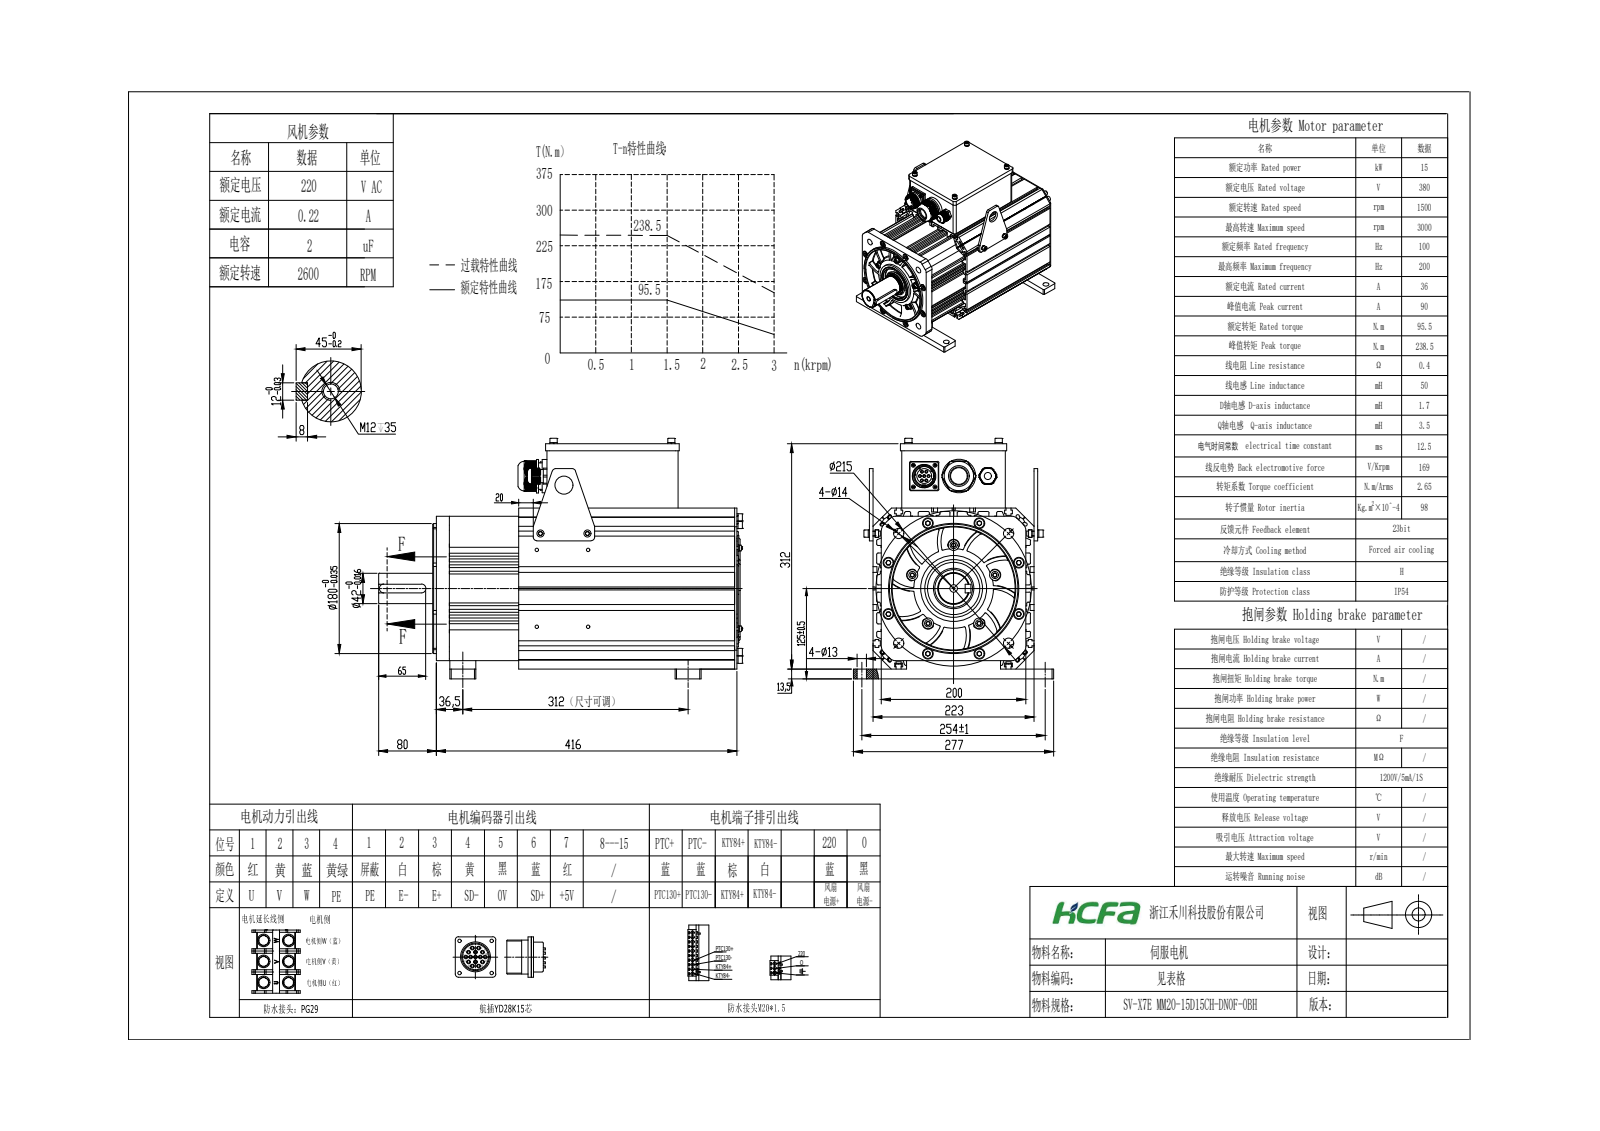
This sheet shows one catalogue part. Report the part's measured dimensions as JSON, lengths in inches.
{"part_name": "15KW", "step_written_by": "SolidWorks 2021 (CONFIG_CONTROL_DESIGN)", "units": "inches", "bodies": {"solids": 111, "faces": 4173, "planar": 2310, "cylindrical": 1117, "other": 746}, "overall_size": [19.827, 13.114, 10.906], "volume_in3": 354.8, "surface_area_in2": 3325, "round_holes": [[0.098, 19], [0.256, 19], [0.263, 19], [0.165, 16], [0.354, 14], [0.591, 10], [0.268, 8], [0.177, 6], [0.551, 5], [0.126, 4], [0.134, 4], [0.173, 4]], "round_bosses_or_shafts": [[0.079, 24], [0.394, 19], [0.389, 19], [0.236, 19], [0.118, 19], [0.138, 15], [0.315, 12], [0.512, 8]], "partial_cylinders_radius": [[0.079, 89], [0.197, 16], [0.059, 8], [0.095, 8], [0.098, 8], [0.118, 8], [0.394, 8], [0.295, 5]], "face_to_face_distances": [8.78, 0.098, 0.453, 0.197, 0.256, 8.327, 8.583, 8.13, 8.071, 0.512], "hole_center_spacings": [3.78, 1.002, 1.547, 1.689, 1.983, 2.083, 2.483, 3.819]}
